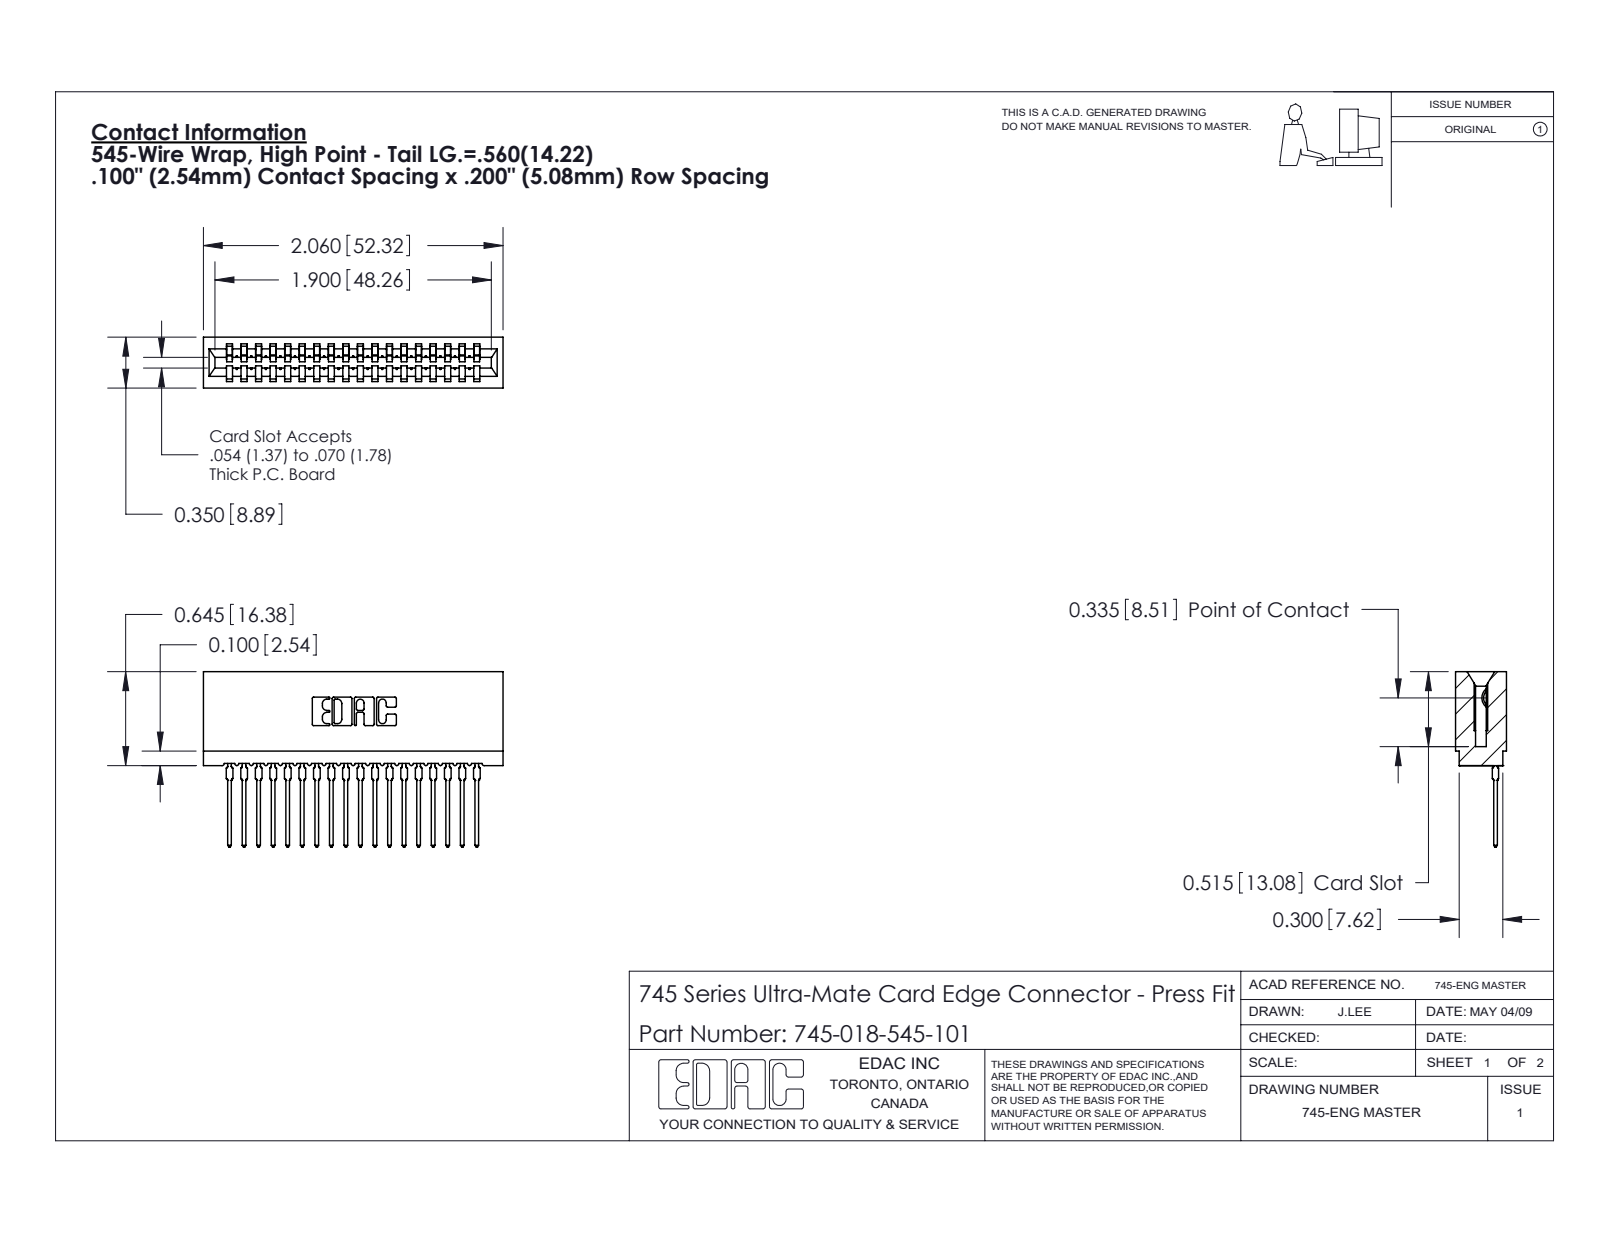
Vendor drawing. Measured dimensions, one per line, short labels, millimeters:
name: 745 Part_Insulator Option - 01; 745-018-545-101; 745-292-001_545
written by: SolidWorks 2020 (CONFIG_CONTROL_DESIGN)
unit: mm
bodies: 19 solids, 2111 faces (1261 planar, 382 cylindrical, 468 other)
size: 52.3 × 30.6 × 8.9
volume: 4 750 mm³; area: 8 632 mm²
rounds: 36× R0.4, 36× R0.5, 22× R0.3, 6× R0.2, 6× R0.8, 4× R0.1, 4× R0.3, 3× R0.7
face distances: 2.5, 5.1, 7.6, 10.2, 12.7, 8.9, 15.2, 17.8, 3.5, 5.4
